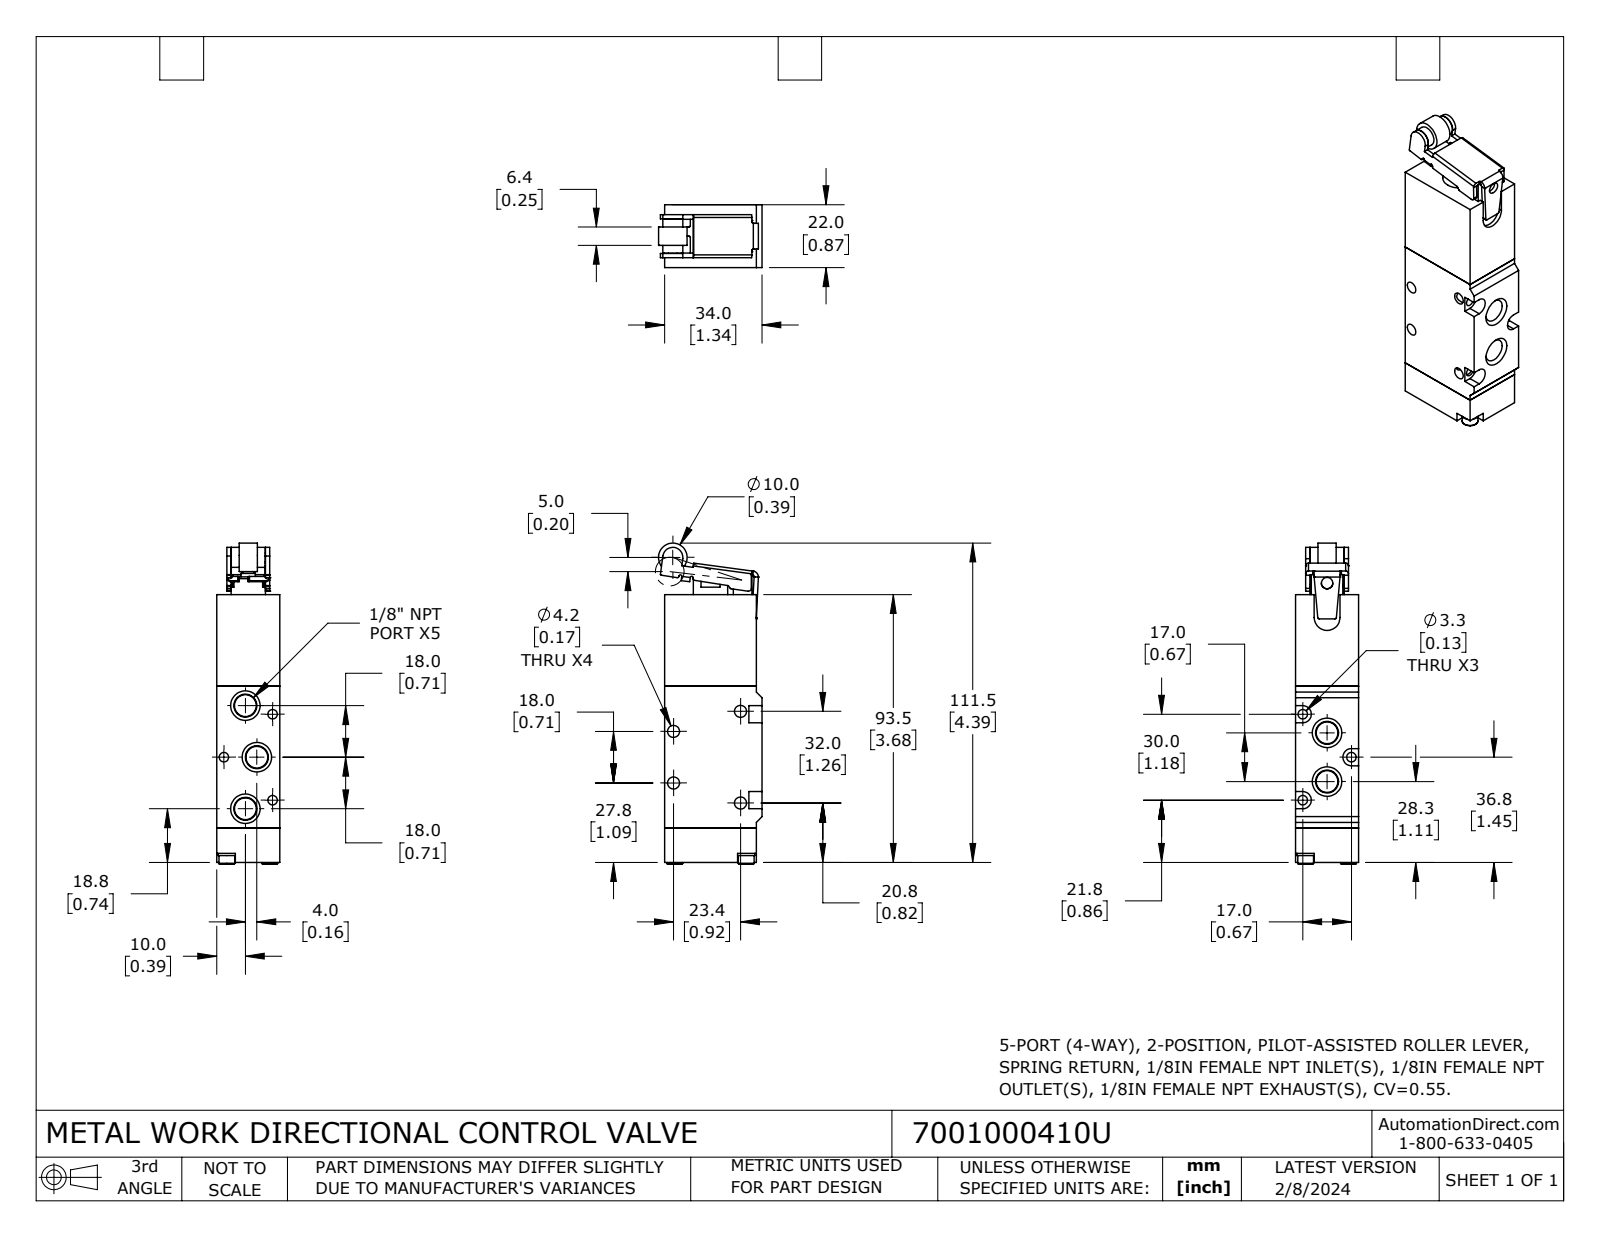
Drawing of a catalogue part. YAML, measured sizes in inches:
part_name: "7001000410U"
step_written_by: "SolidWorks 2023 (CONFIG_CONTROL_DESIGN)"
units: inches
bodies: {solids: 8, faces: 295, planar: 143, cylindrical: 100, other: 52}
overall_size: [4.414, 1.423, 0.866]
volume: 4.065
surface_area: 32.46
round_holes:
  - {diameter: 0.165, count: 4}
  - {diameter: 0.13, count: 3}
  - {diameter: 0.118, count: 2}
  - {diameter: 0.157, count: 1}
round_bosses_or_shafts:
  - {diameter: 0.236, count: 2}
  - {diameter: 0.217, count: 2}
  - {diameter: 0.472, count: 1}
  - {diameter: 0.394, count: 1}
  - {diameter: 0.276, count: 1}
  - {diameter: 0.197, count: 1}
  - {diameter: 0.12, count: 1}
  - {diameter: 0.118, count: 1}
partial_cylinders:
  - {radius: 0.02, count: 15}
  - {radius: 0.004, count: 4}
  - {radius: 0.039, count: 4}
  - {radius: 0.118, count: 3}
  - {radius: 0.059, count: 2}
  - {radius: 0.079, count: 1}
  - {radius: 0.177, count: 1}
face_to_face_distances: [0.866, 1.26, 1.949, 0.059, 0.472, 0.079, 1.339, 2.421, 0.138, 3.681]
hole_center_spacings: [0.893, 0.961, 1.348, 0.709, 1.148, 1.181, 1.26]
